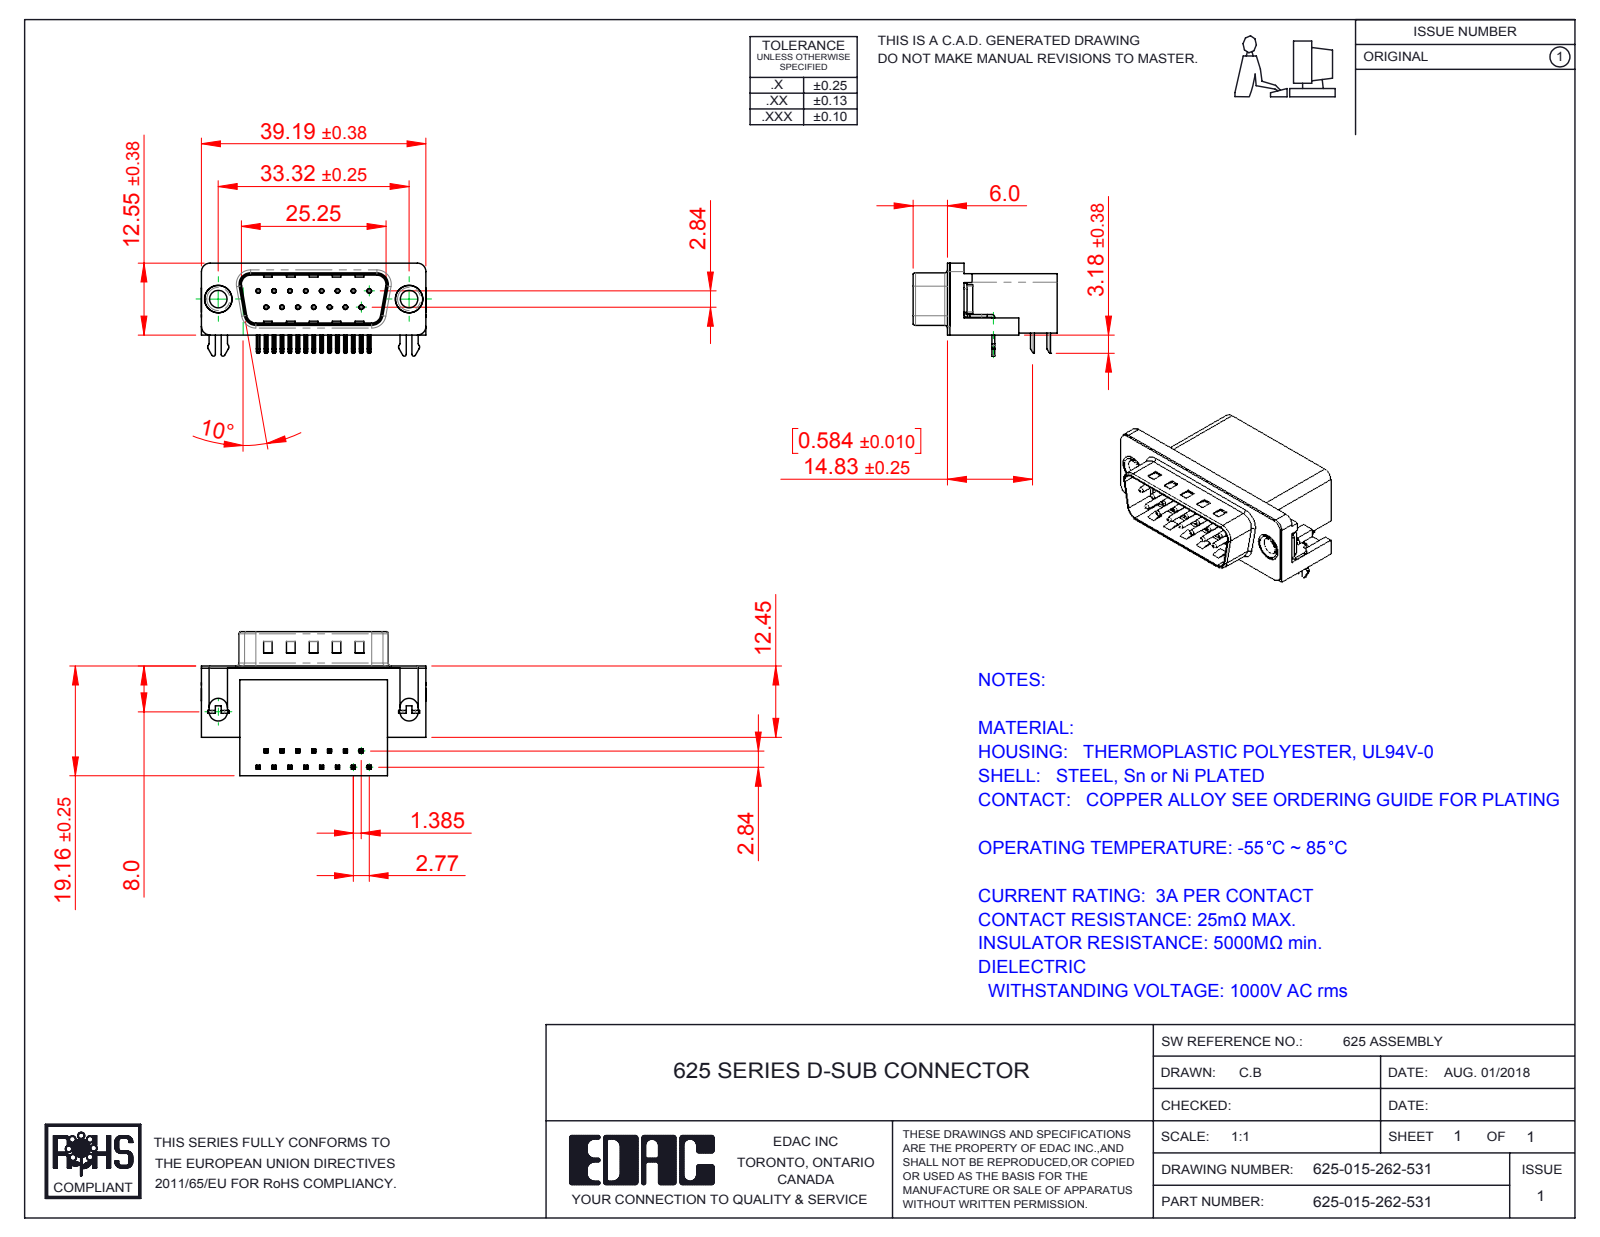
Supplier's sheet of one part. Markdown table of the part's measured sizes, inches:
| quantity | value |
| --- | --- |
| part name | 625 Housing_15 Socket; 625 2 Prong Board Lock; 625 Contact Top; 625 Contact Bottom (+3 more) |
| STEP written by | SolidWorks 2016 (CONFIG_CONTROL_DESIGN) |
| units | inches |
| bodies | 21 solids, 1479 faces (925 planar, 437 cylindrical, 117 other) |
| overall size | 1.544 × 0.991 × 0.64 |
| volume | 0.38 in³ |
| surface area | 9.931 in² |
| round holes (diameter × count) | 0.014 × 15, 0.031 × 15, 0.12 × 2, 0.157 × 2, 0.189 × 2, 0.197 × 2 |
| round bosses / shafts (diameter × count) | 0.03 × 15, 0.193 × 2, 0.187 × 2, 0.152 × 2 |
| partial cylindrical surfaces (radius × count) | 0.01 × 68, 0.005 × 30, 0.039 × 16, 0.02 × 14, 0.063 × 8, 0.059 × 6, 0.013 × 4, 0.035 × 4 |
| main face-to-face distances | 0.016, 0.407, 0.739, 0.083, 0.754, 0.412, 0.067, 0.428, 0.345, 0.64 |
| hole center spacings | 0.124, 0.109, 0.218, 0.327, 0.436, 0.198, 0.198, 0.294 |
